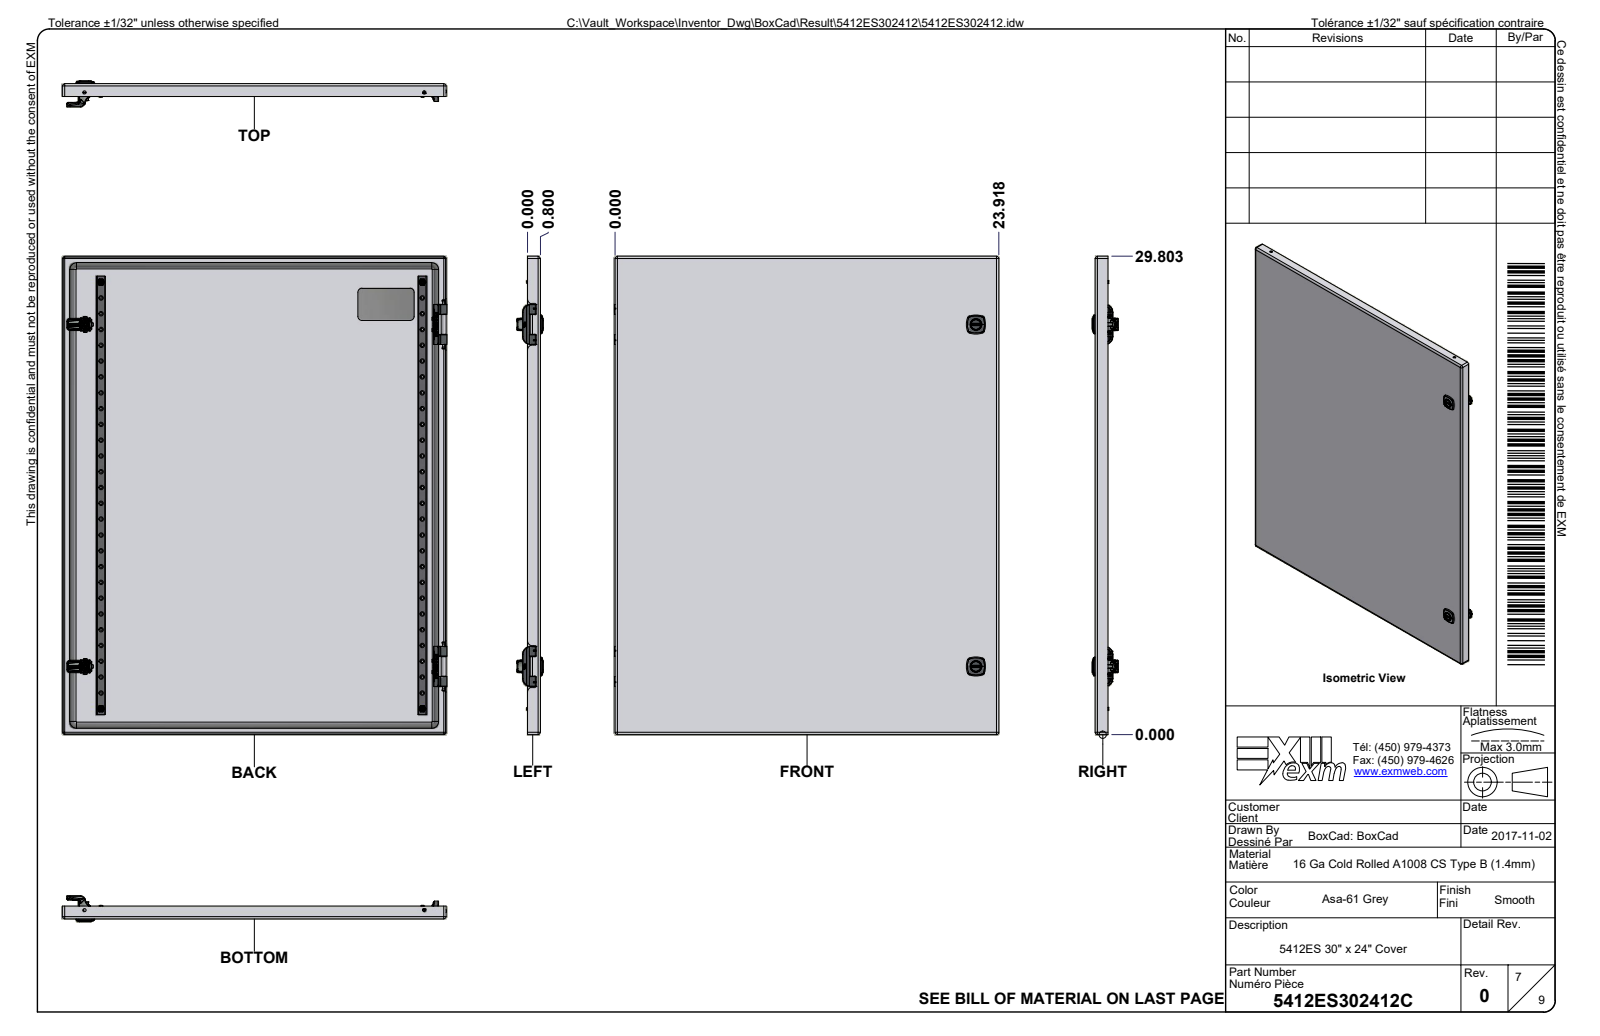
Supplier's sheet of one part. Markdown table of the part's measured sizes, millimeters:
| quantity | value |
| --- | --- |
| part name | 5412ES302412; 5412ES302412B; 5412ES302412B-P; STK-Q-16005 (+8 more) |
| STEP written by | Autodesk Inventor 2024 (AUTOMOTIVE_DESIGN) |
| units | millimeters |
| bodies | 64 solids, 10122 faces (3061 planar, 2571 cylindrical, 4490 other) |
| overall size | 762 × 609.7 × 338.1 |
| volume | 3 976 000 mm³ |
| surface area | 4 977 000 mm² |
| round holes (diameter × count) | 4.2 × 52, 0.8 × 9, 1.1 × 8, 5.1 × 8, 8 × 8, 7.9 × 6, 4.5 × 4, 5 × 4, 6.8 × 4, 6.9 × 4, 7.4 × 4, 9.9 × 4 |
| round bosses / shafts (diameter × count) | 6 × 52, 5.9 × 9, 0.8 × 9, 1 × 8, 18.2 × 4, 9.5 × 4, 7.9 × 4, 6.7 × 4 |
| partial cylindrical surfaces (radius × count) | 0.5 × 263, 0.3 × 139, 1 × 97, 0.2 × 94, 0.3 × 50, 0.8 × 32, 0.4 × 30, 2.1 × 24 |
| main face-to-face distances | 1.3, 332.3, 330.9, 608.3, 333.6, 23.5, 22.2, 308.7, 310.1, 26.2 |
| hole center spacings | 50, 25, 75, 100, 125, 150, 175, 541.1 |
